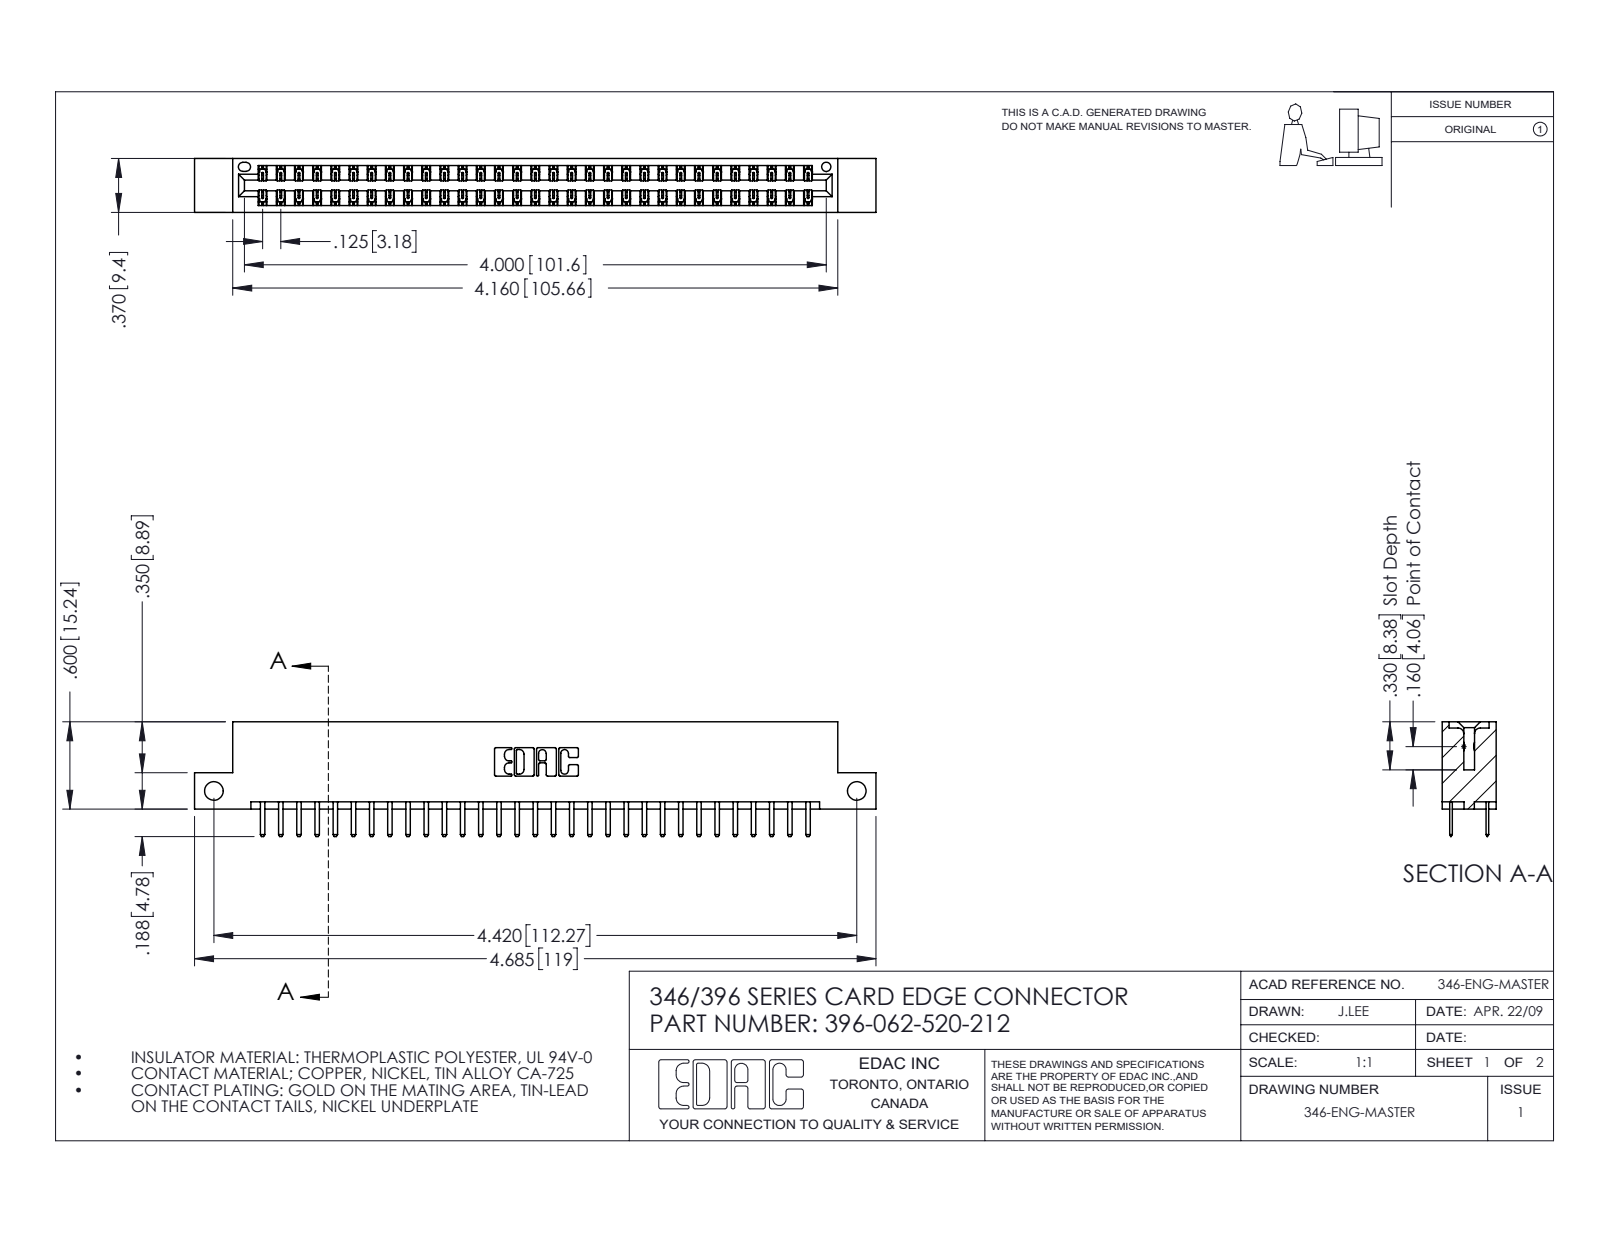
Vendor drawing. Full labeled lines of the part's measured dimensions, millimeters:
Part name (STEP PRODUCT): 396-062-520-212; 345-292-001_345-293-120; 346 Part_Flush Mounting Lugs - Side Mount
STEP written by: SolidWorks 2016 (CONFIG_CONTROL_DESIGN)
Units: millimetres
Bodies: 63 solids, 3594 faces (2370 planar, 1224 cylindrical, 0 other)
Overall size (bounding box): 119 × 20 × 9.4
Volume: 11 400 mm³ · Surface area: 15 300 mm²
Round holes (diameter × count): ⌀3.3 ×2, ⌀1.6 ×1
Partial cylindrical surfaces — rounded edges, fillets, slot ends (radius × count): R0.2 ×93, R0.3 ×66, R0.3 ×22, R0.2 ×6, R0.8 ×6, R0.7 ×3, R0.4 ×2, R0.6 ×2
Main face-to-face distances: 1.2, 8.2, 6.4, 9.4, 7, 1.8, 7.6, 0.6, 3.8, 5.6
Hole centre spacings: 112.3
